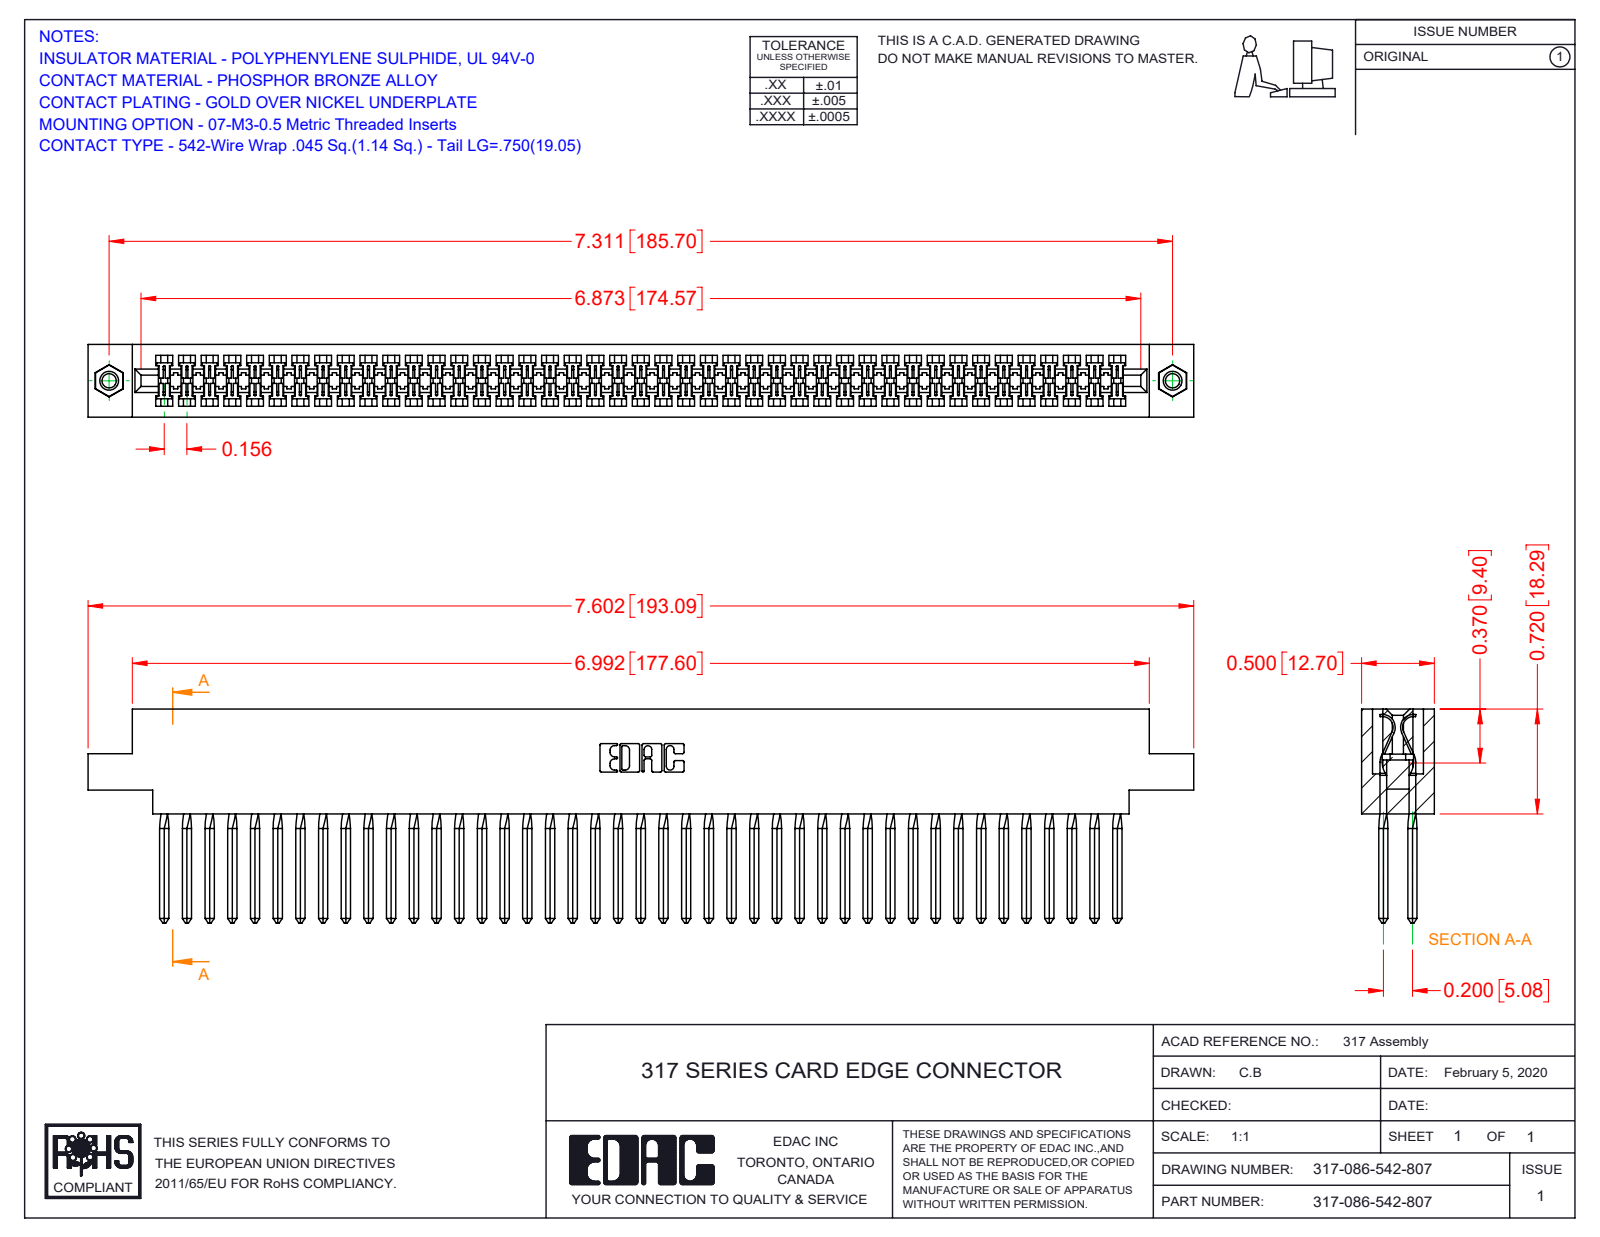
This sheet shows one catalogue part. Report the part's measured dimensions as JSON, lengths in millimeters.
{"part_name": "317-086-542-807; 317 Part_.156 Dia - TI; 317-290-003_542; 345-250-001_345-250-005-103", "step_written_by": "SolidWorks 2016 (CONFIG_CONTROL_DESIGN)", "units": "millimeters", "bodies": {"solids": 89, "faces": 5064, "planar": 4046, "cylindrical": 658, "other": 360}, "overall_size": [193.1, 37.3, 12.7], "volume_mm3": 31640, "surface_area_mm2": 44060, "round_holes": [[2.5, 2], [3.2, 2], [4, 2]], "round_bosses_or_shafts": [[3.9, 2]], "partial_cylinders_radius": [[0.2, 172], [0.3, 22], [0.2, 6], [0.8, 6], [0.7, 3], [1.9, 2], [2.3, 2], [2.5, 2]], "face_to_face_distances": [12.7, 1.9, 10.8, 8.9, 5.1, 1.2, 3.3, 9.4, 1.3, 7.5], "hole_center_spacings": [185.7]}
